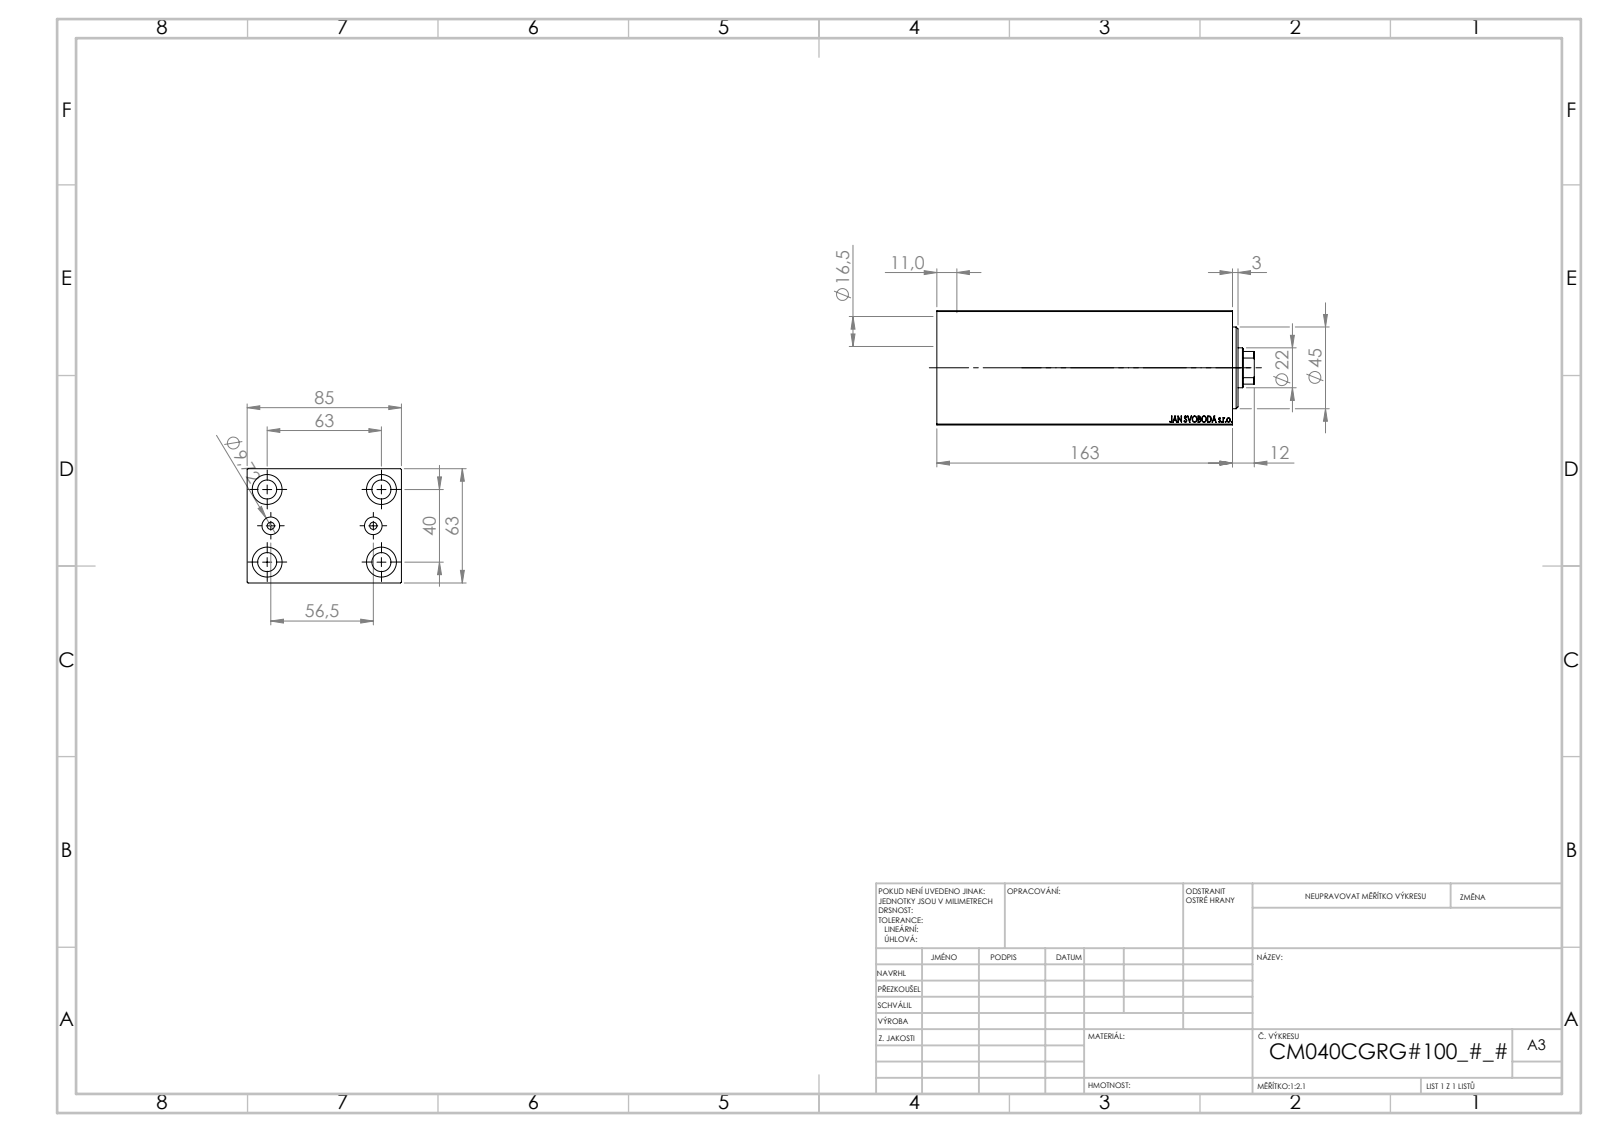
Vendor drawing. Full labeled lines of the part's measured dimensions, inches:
Part name (STEP PRODUCT): V450CM_C_Body; V450CM_C_VCP; V450CM_VC_B
STEP written by: SolidWorks 2019 (CONFIG_CONTROL_DESIGN)
Units: inches
Bodies: 3 solids, 858 faces (408 planar, 56 cylindrical, 394 other)
Overall size (bounding box): 6.89 × 3.346 × 2.48
Volume: 43.76 in³ · Surface area: 187.3 in²
Round holes (diameter × count): ⌀0.413 ×4, ⌀0.65 ×4, ⌀0.157 ×2, ⌀0.383 ×2, ⌀0.492 ×1, ⌀0.866 ×1, ⌀1.004 ×1, ⌀1.575 ×1, ⌀1.654 ×1, ⌀1.772 ×1
Partial cylindrical surfaces — rounded edges, fillets, slot ends (radius × count): R0.413 ×1
Main face-to-face distances: 2.48, 3.346, 6.417, 5.049, 1.368, 0.394, 6.024, 4.656, 0.433, 5.984
Hole centre spacings: 0.798, 1.469, 2.481, 1.112, 1.575, 2.48, 2.938, 2.224
